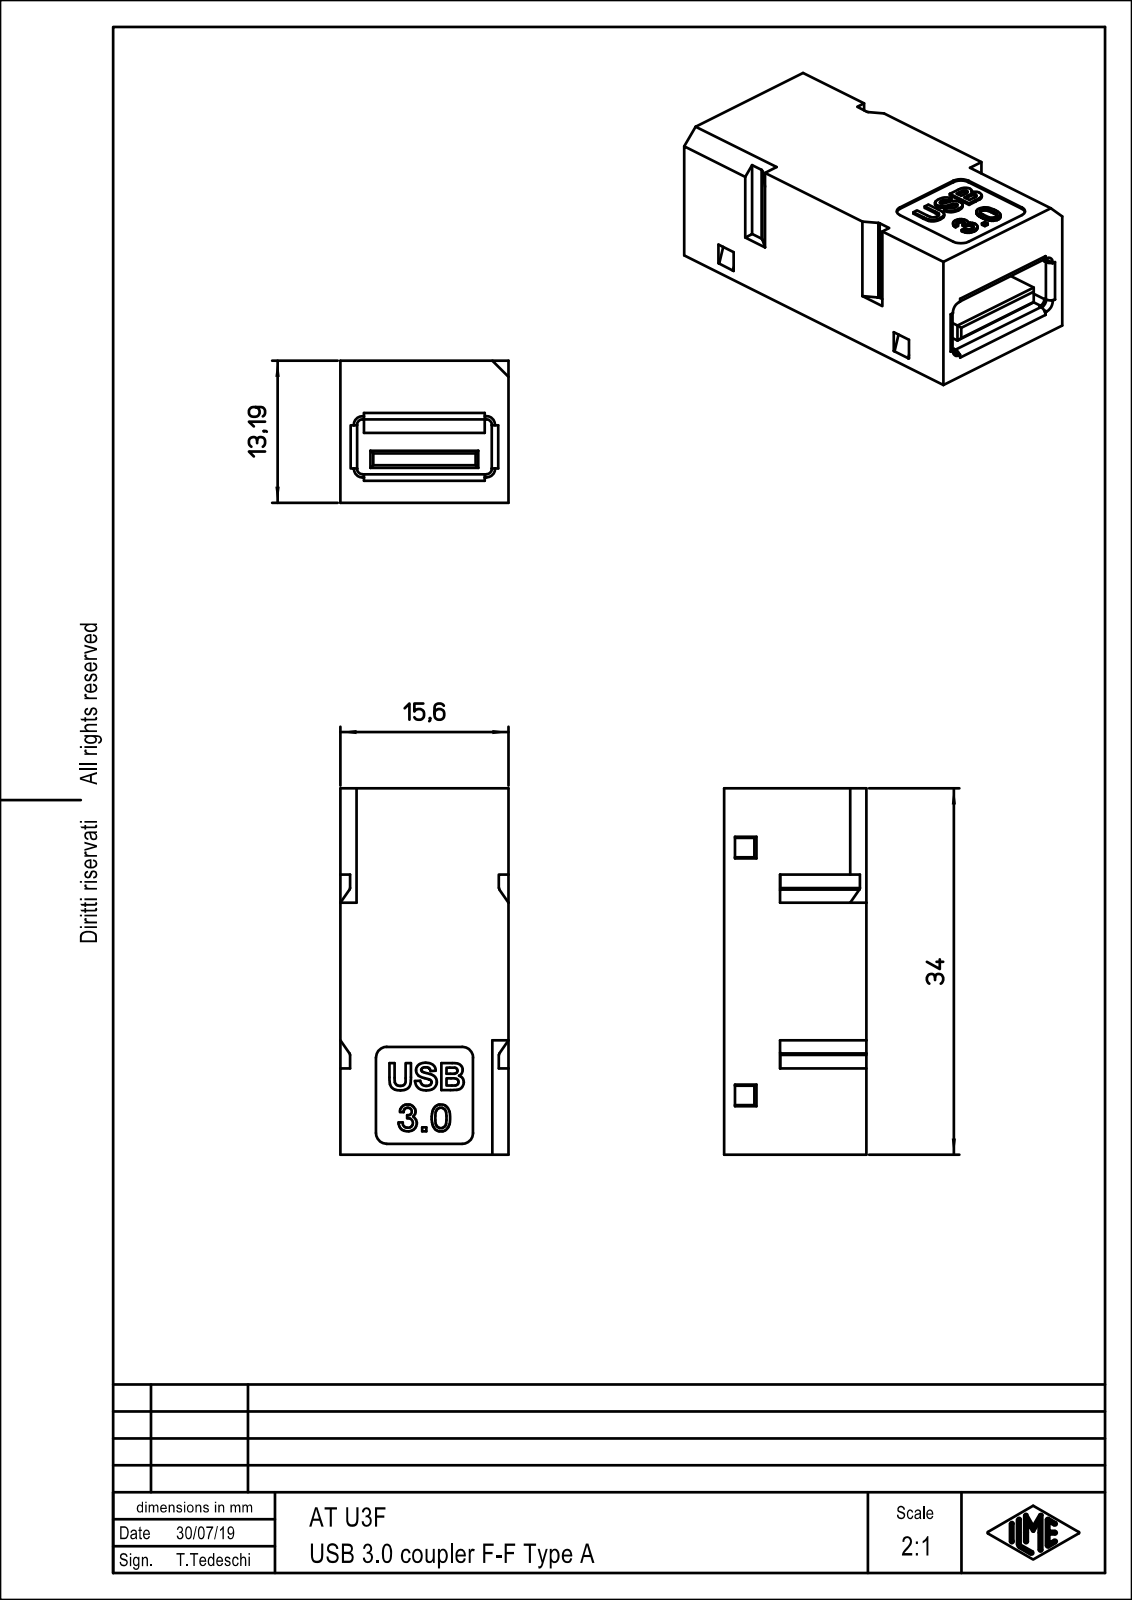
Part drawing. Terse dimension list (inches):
name: AF_U3F
written by: Creo Elements/Direct Modeling 20.1B 02-Apr-2019 (C) Parametric Technology GmbH (AUTOMOTIVE_DESIGN)
unit: in
bodies: 1 solid, 401 faces (334 planar, 34 cylindrical, 33 other)
size: 1.339 × 0.614 × 0.519
volume: 0.341 in³; area: 6.46 in²
rounds: 8× R0.024, 4× R0.01, 4× R0.02, 4× R0.031, 4× R0.039, 2× R0.012
face distances: 0.519, 0.614, 0.415, 0.104, 0.215, 0.201, 0.305, 0.087, 0.024, 0.177
